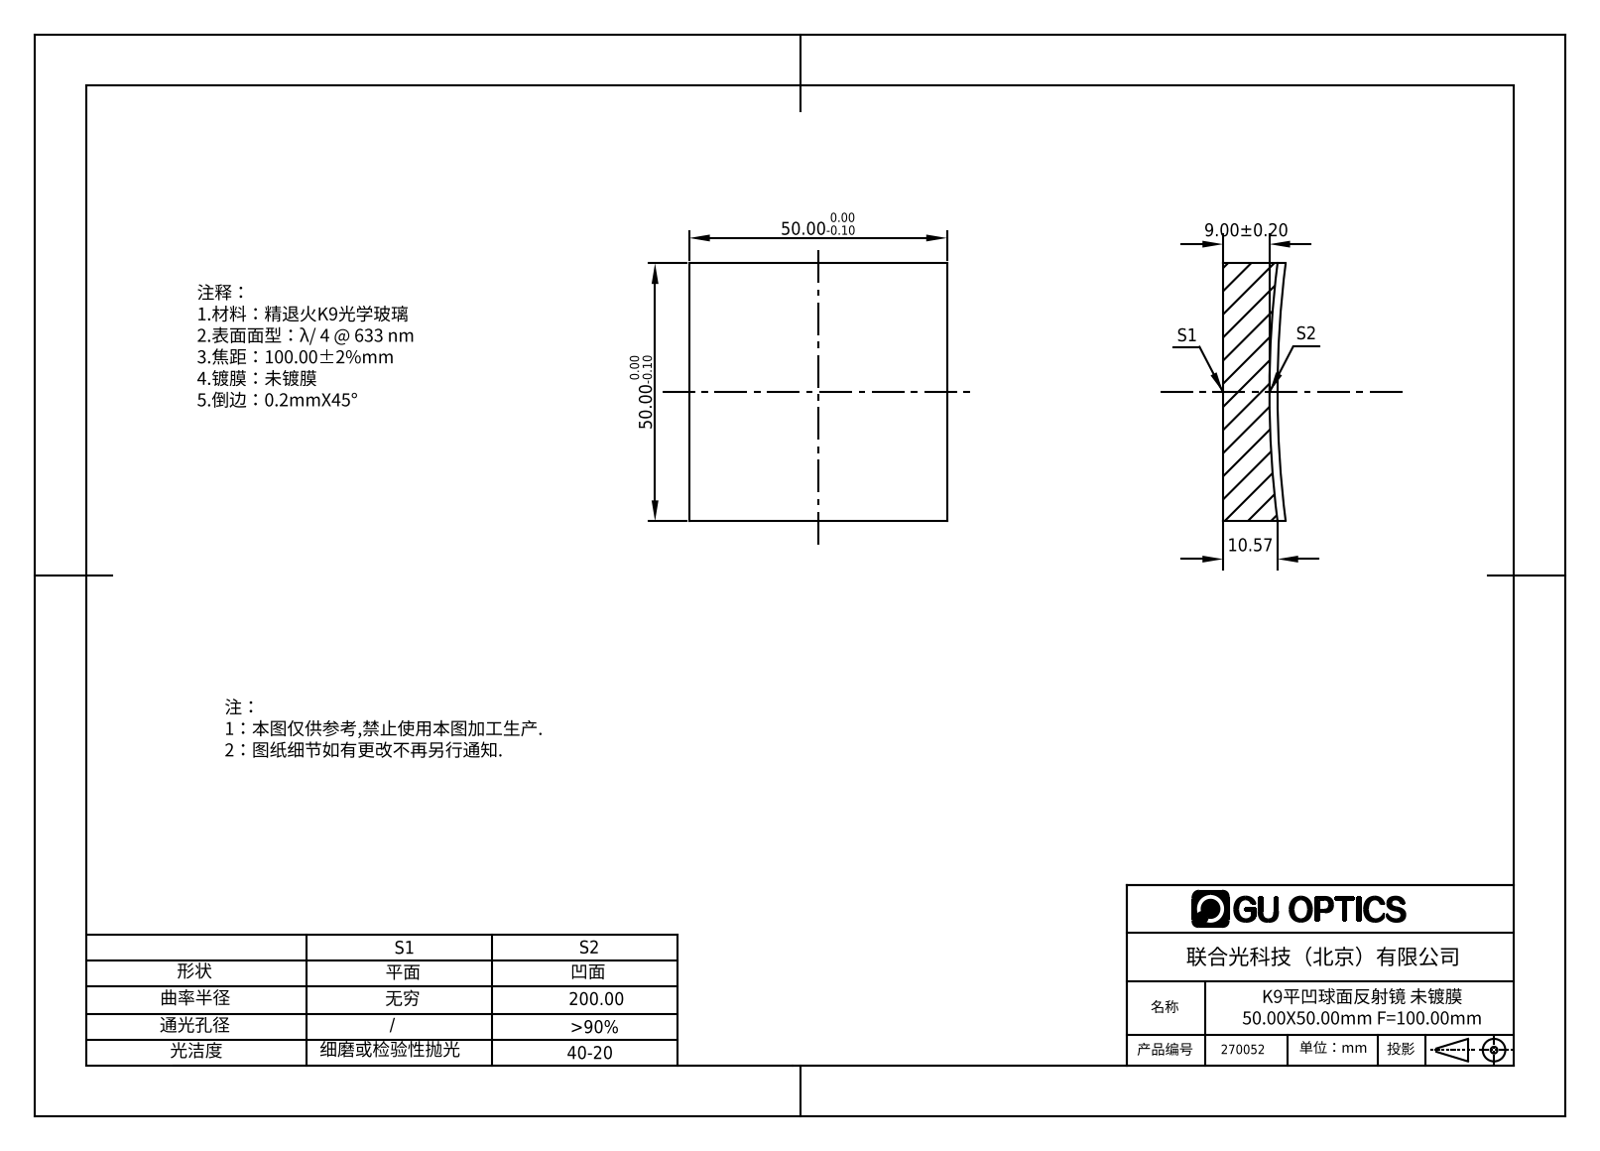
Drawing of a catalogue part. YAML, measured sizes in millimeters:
part_name: "270052"
step_written_by: "SolidWorks 2019 (AUTOMOTIVE_DESIGN)"
units: millimeters
bodies: {solids: 1, faces: 7, planar: 5, cylindrical: 0, other: 2}
overall_size: [50, 50, 12.15]
volume: 25114
surface_area: 7232
face_to_face_distances: [50]
